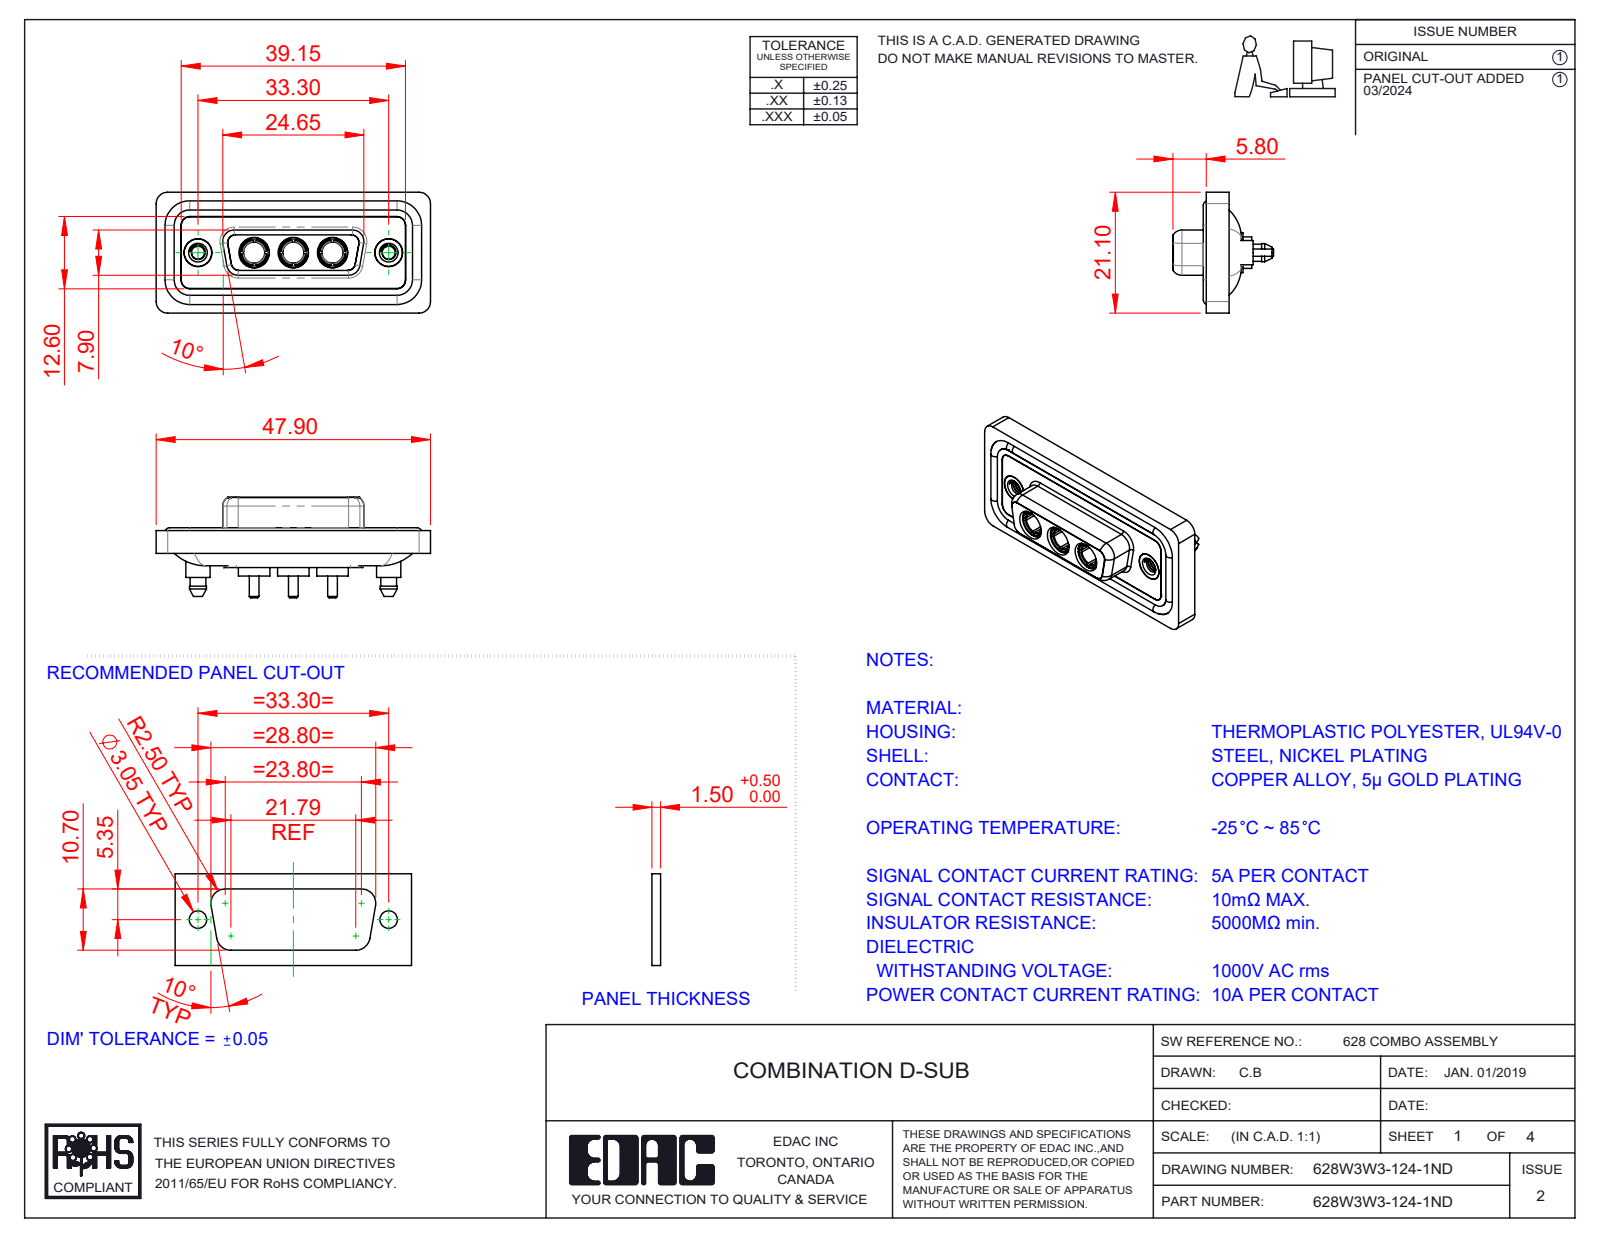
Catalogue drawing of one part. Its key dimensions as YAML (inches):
part_name: "628W3W3-124-1ND; Power Socket_10A S; 628Combo Shell Rear_15 Contacts; 628Combo Housing_3W3 (+3 more)"
step_written_by: "SolidWorks 2023 (CONFIG_CONTROL_DESIGN)"
units: inches
bodies: {solids: 13, faces: 674, planar: 208, cylindrical: 305, other: 161}
overall_size: [1.886, 0.831, 0.691]
volume: 0.373
surface_area: 15.56
round_holes:
  - {diameter: 0.191, count: 5}
  - {diameter: 0.146, count: 3}
  - {diameter: 0.209, count: 3}
  - {diameter: 0.089, count: 2}
  - {diameter: 0.157, count: 2}
  - {diameter: 0.159, count: 2}
  - {diameter: 0.197, count: 2}
round_bosses_or_shafts:
  - {diameter: 0.063, count: 4}
  - {diameter: 0.217, count: 3}
  - {diameter: 0.205, count: 3}
  - {diameter: 0.195, count: 3}
  - {diameter: 0.187, count: 3}
  - {diameter: 0.148, count: 3}
  - {diameter: 0.067, count: 3}
  - {diameter: 0.213, count: 2}
partial_cylinders:
  - {radius: 0.059, count: 24}
  - {radius: 0.079, count: 20}
  - {radius: 0.053, count: 12}
  - {radius: 0.063, count: 10}
  - {radius: 0.01, count: 4}
  - {radius: 0.02, count: 4}
  - {radius: 0.024, count: 4}
  - {radius: 0.026, count: 4}
face_to_face_distances: [0.016, 0.071, 0.063, 0.02, 0.293, 0.043, 0.114, 0.222, 0.278, 0.059]
hole_center_spacings: [0.27, 0.386, 0.656, 0.925, 0.539, 1.311]
